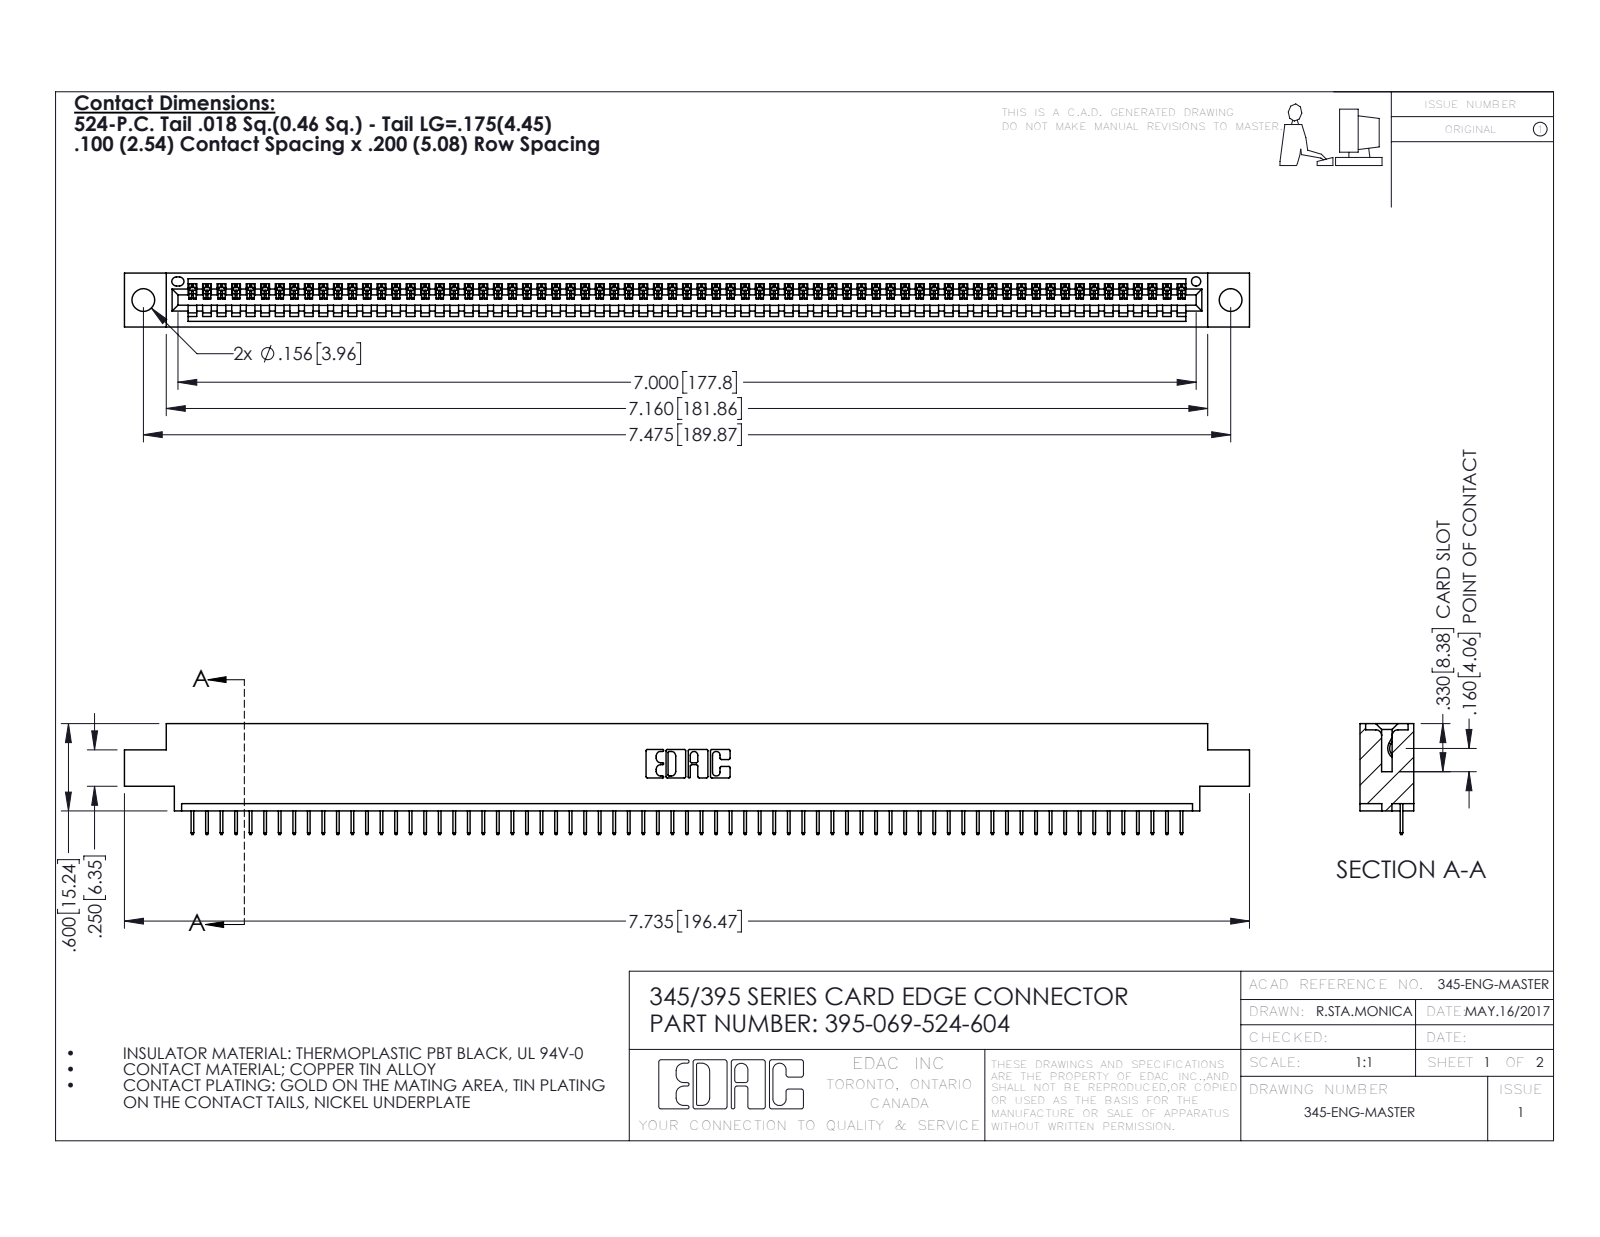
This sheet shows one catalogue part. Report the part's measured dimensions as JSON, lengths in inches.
{"part_name": "395-069-524-604; 345 Part_0.170 Offset - 0.156 Dia-TH; 345-292-001_345-293-124", "step_written_by": "SolidWorks 2016 (CONFIG_CONTROL_DESIGN)", "units": "inches", "bodies": {"solids": 70, "faces": 4408, "planar": 3258, "cylindrical": 1150, "other": 0}, "overall_size": [7.735, 0.762, 0.37], "volume_in3": 1.123, "surface_area_in2": 37.04, "round_holes": [[0.156, 2], [0.064, 1]], "partial_cylinders_radius": [[0.006, 138], [0.01, 22], [0.007, 6], [0.031, 6], [0.026, 3], [0.031, 2], [0.04, 2], [0.014, 1]], "face_to_face_distances": [0.072, 0.298, 0.37, 0.2, 0.098, 0.272, 0.025, 0.225, 0.072, 0.175], "hole_center_spacings": [0.27, 7.239, 7.475]}
